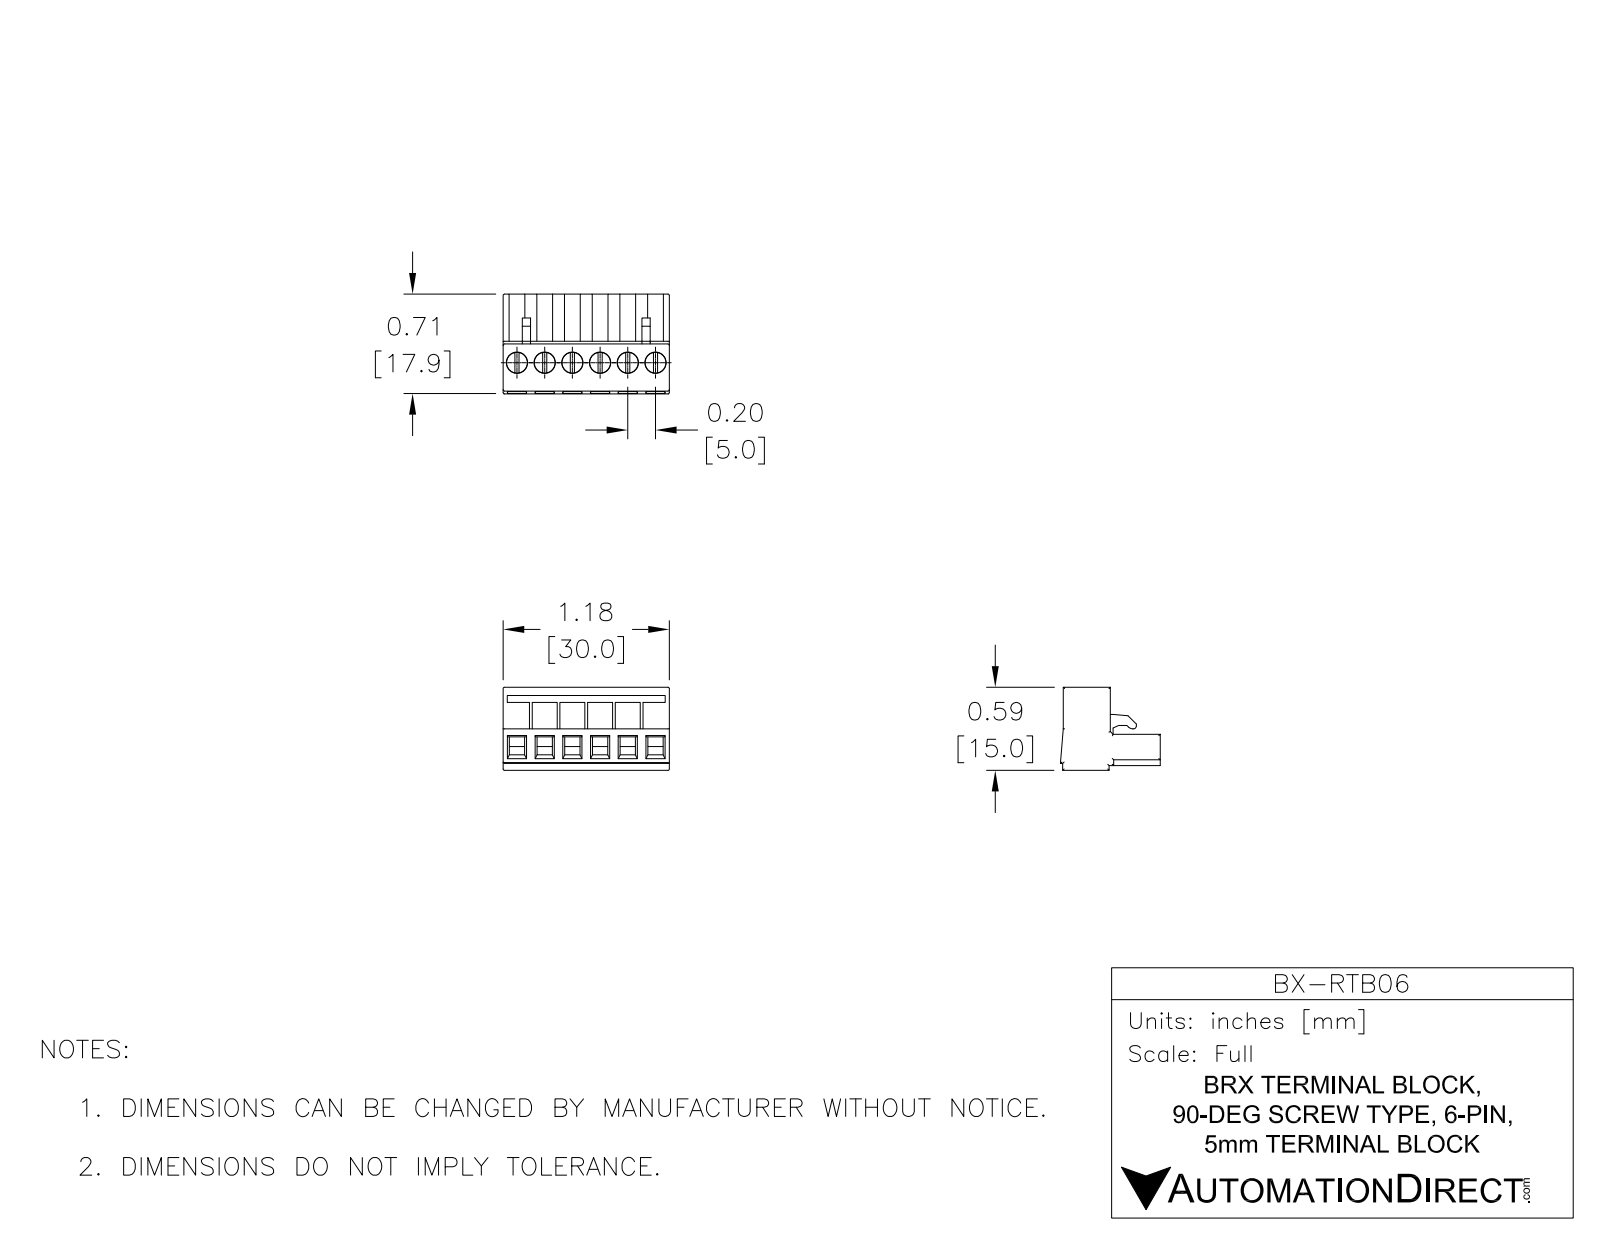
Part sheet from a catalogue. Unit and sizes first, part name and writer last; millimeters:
Units: millimetres
Overall size (bounding box): 30 × 18 × 15
Round holes (diameter × count): ⌀1.6 ×6, ⌀3.15 ×6, ⌀3.85 ×6
Round bosses / shafts (diameter × count): ⌀3.75 ×6
Partial cylindrical surfaces — rounded edges, fillets, slot ends (radius × count): R0.25 ×29, R2.53 ×6, R0.5 ×1, R1 ×1
Main face-to-face distances: 8.5, 15, 5.7, 9.3, 6.5, 30, 9, 0.8, 9.85, 17.5
Hole centre spacings: 5, 10, 15, 20, 25
Volume: 4 578 mm³ · Surface area: 3 587 mm²
Bodies: 1 solid, 333 faces (229 planar, 92 cylindrical, 12 other)
Part name (STEP PRODUCT): BX-RTB06
STEP written by: SolidWorks 2016 (AUTOMOTIVE_DESIGN)
